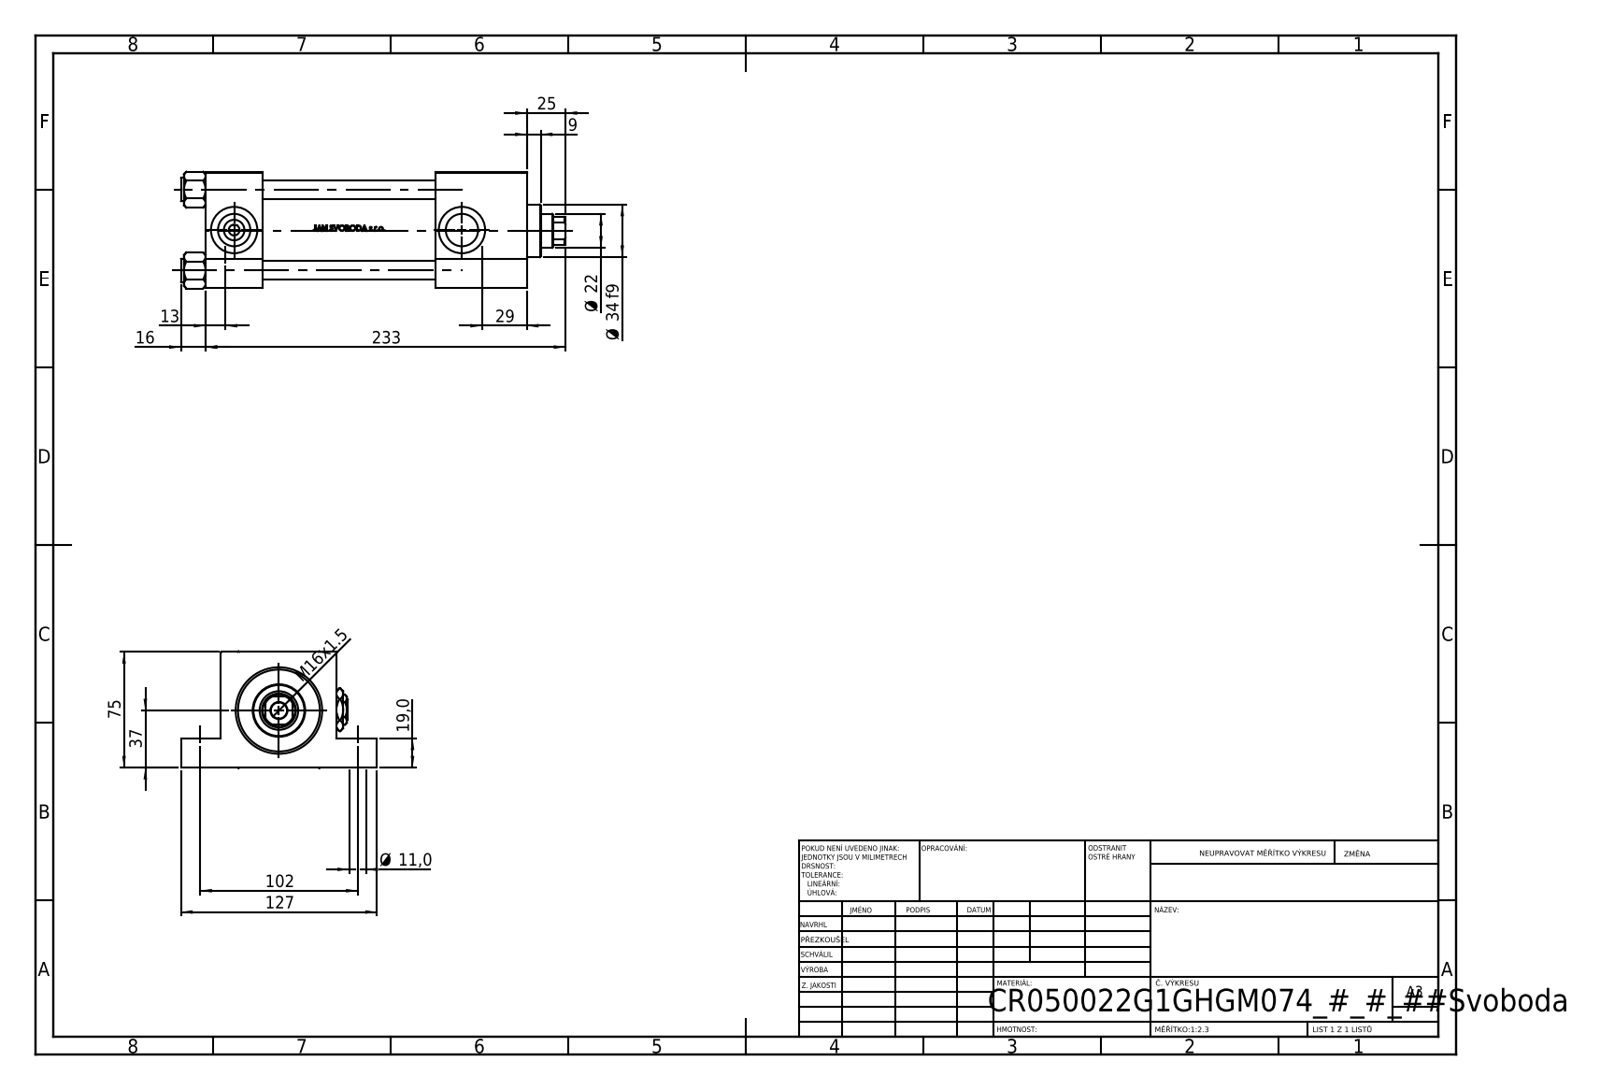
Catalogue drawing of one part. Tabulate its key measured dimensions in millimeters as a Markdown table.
| quantity | value |
| --- | --- |
| part name | NUT_M5_G; V215CR_VCP_G; Zatka_pro_OIL_PORT; V215CR_G_Body (+2 more) |
| STEP written by | SolidWorks 2019 (CONFIG_CONTROL_DESIGN) |
| units | millimeters |
| bodies | 12 solids, 1134 faces (454 planar, 128 cylindrical, 552 other) |
| overall size | 249 × 127 × 75.54 |
| volume | 824 333 mm³ |
| surface area | 191 161 mm² |
| round holes (diameter × count) | 11 × 4, 12 × 4, 7 × 2, 20.96 × 2, 30 × 2, 10.5 × 1, 22 × 1, 25 × 1, 41 × 1, 50 × 1, 53 × 1 |
| round bosses / shafts (diameter × count) | 15 × 4, 56 × 1, 34 × 1 |
| partial cylindrical surfaces (radius × count) | 10.5 × 1 |
| main face-to-face distances | 75, 37, 208, 171, 19, 56, 149, 112, 59, 26 |
| hole center spacings | 52.3, 36.63, 37.34, 73.96, 102, 166, 194.83, 147.5 |
